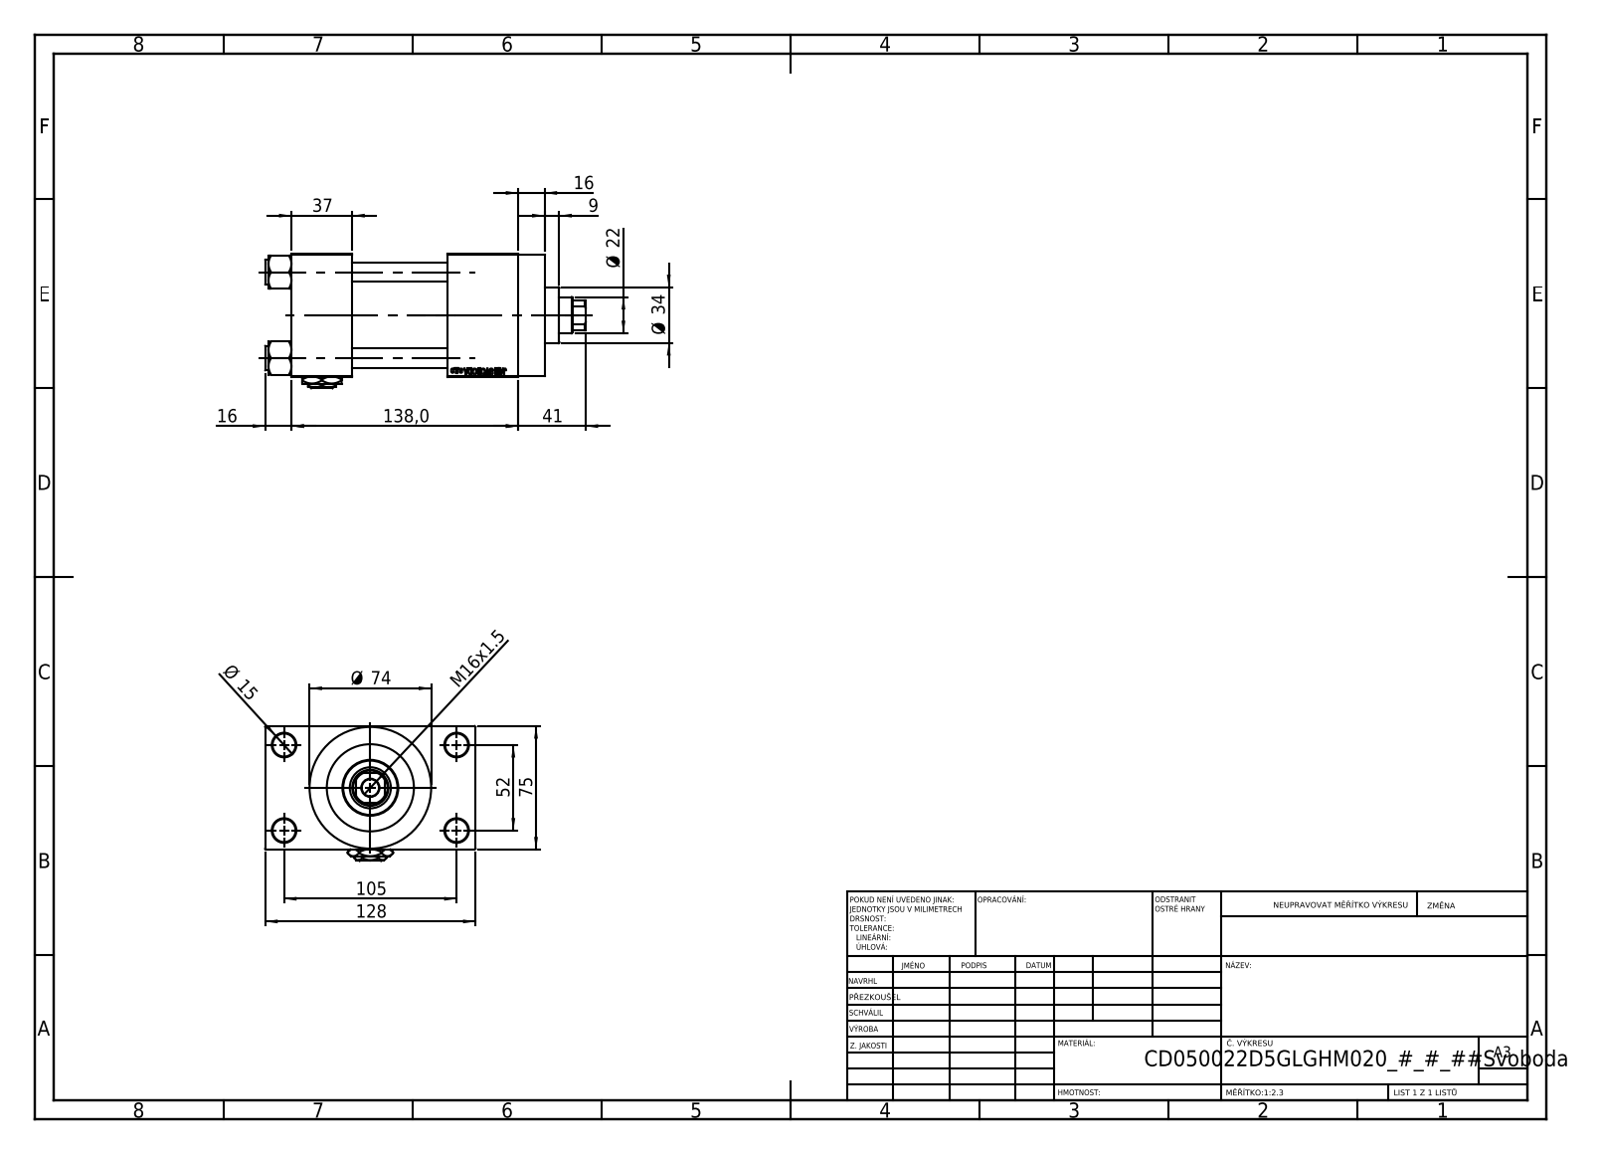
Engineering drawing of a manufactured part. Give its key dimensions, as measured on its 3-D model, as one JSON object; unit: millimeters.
{"part_name": "V215CD_VC_A; V215CD_D_Body; Zatka_pro_OIL_PORT; V215CD_D_TYCINKA (+2 more)", "step_written_by": "SolidWorks 2019 (CONFIG_CONTROL_DESIGN)", "units": "millimeters", "bodies": {"solids": 12, "faces": 1146, "planar": 519, "cylindrical": 89, "other": 538}, "overall_size": [195, 128, 82], "volume_mm3": 809306, "surface_area_mm2": 166407, "round_holes": [[12, 4], [14, 4], [7, 2], [20.96, 2], [30, 2], [10.5, 1], [22, 1], [25, 1], [41, 1], [50, 1], [53, 1]], "round_bosses_or_shafts": [[15, 4], [74, 1], [56, 1], [34, 1]], "partial_cylinders_radius": [[10.5, 1]], "face_to_face_distances": [75, 58, 37, 95, 26.5, 101.5, 43, 138, 101, 16], "hole_center_spacings": [26.35, 36.98, 52.3, 58.43, 58.59, 78.65, 94.37, 52]}
